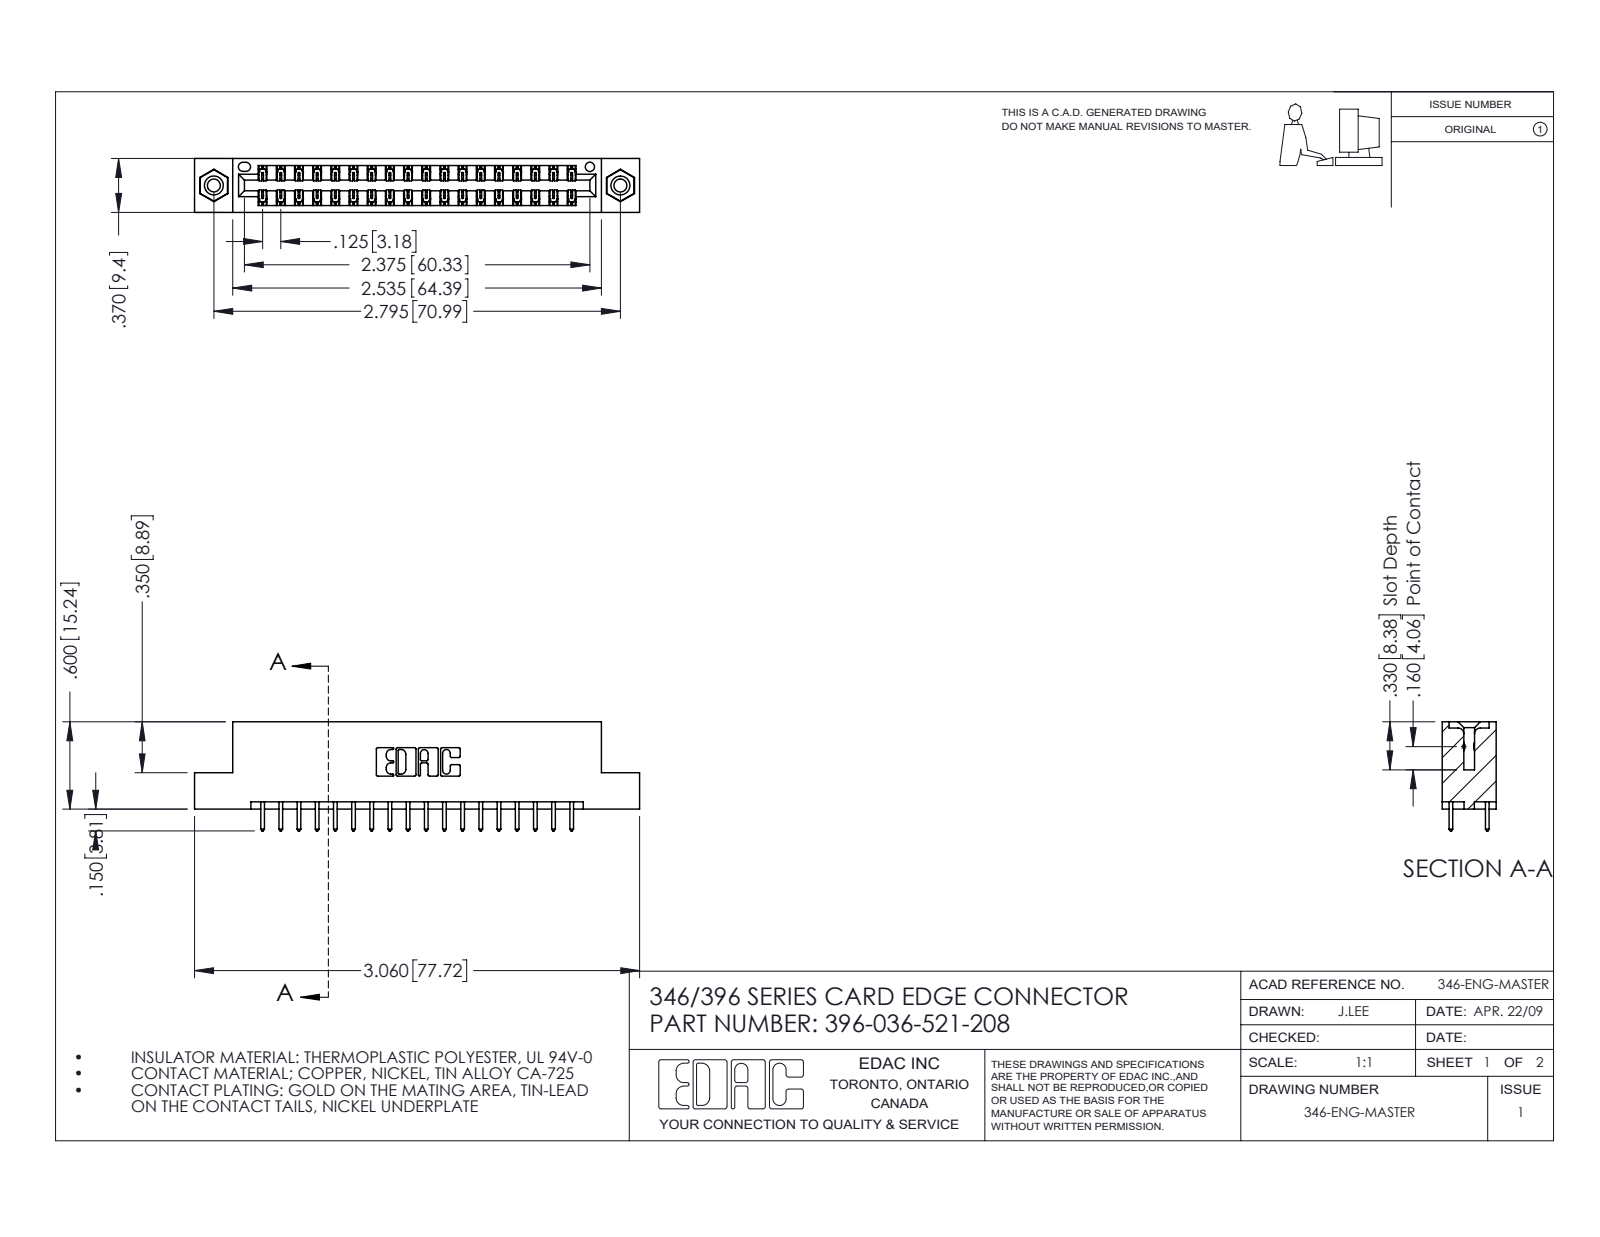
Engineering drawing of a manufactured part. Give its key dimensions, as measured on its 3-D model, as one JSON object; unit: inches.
{"part_name": "345-292-001_345-293-121; 346 Part_Flush Mounting Lugs - 0.156 Dia-TI; 396-036-521-208; 345-250-001_345-250-003-102", "step_written_by": "SolidWorks 2016 (CONFIG_CONTROL_DESIGN)", "units": "inches", "bodies": {"solids": 39, "faces": 2054, "planar": 1368, "cylindrical": 670, "other": 16}, "overall_size": [3.06, 0.75, 0.37], "volume_in3": 0.45, "surface_area_in2": 15, "round_holes": [[0.089, 2], [0.125, 2], [0.156, 2], [0.064, 1]], "round_bosses_or_shafts": [[0.155, 2]], "partial_cylinders_radius": [[0.006, 54], [0.01, 36], [0.01, 22], [0.007, 6], [0.031, 6], [0.026, 3], [0.014, 2], [0.022, 2]], "face_to_face_distances": [0.048, 0.322, 0.25, 0.37, 0.072, 0.298, 0.025, 0.275, 0.148, 0.222], "hole_center_spacings": [0.246, 2.588, 2.795]}
